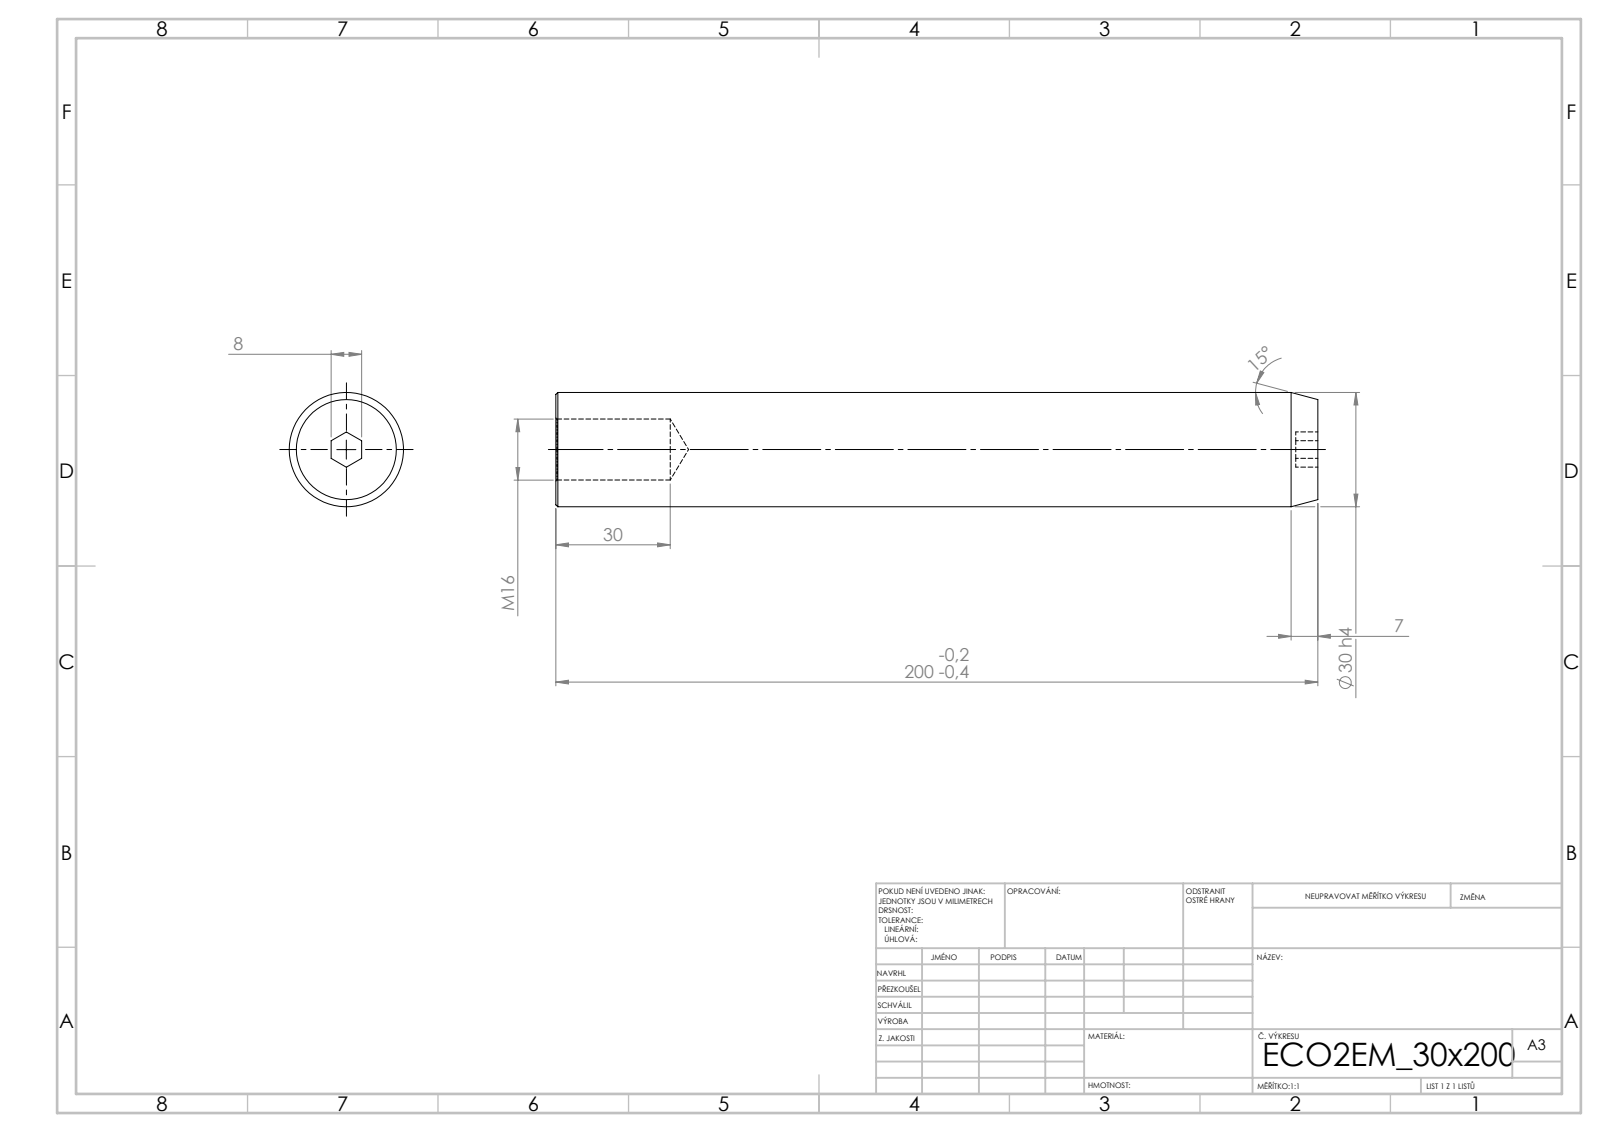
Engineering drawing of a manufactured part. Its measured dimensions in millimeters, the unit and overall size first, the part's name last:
Units: millimetres
Overall size (bounding box): 200 × 30 × 30
Round holes (diameter × count): ⌀16 ×1
Round bosses / shafts (diameter × count): ⌀30 ×1
Main face-to-face distances: 200, 8, 5.8, 194.2
Volume: 134 091 mm³ · Surface area: 21 746 mm²
Bodies: 1 solid, 21 faces (9 planar, 4 cylindrical, 8 other)
STEP written by: SolidWorks 2019 (CONFIG_CONTROL_DESIGN)
